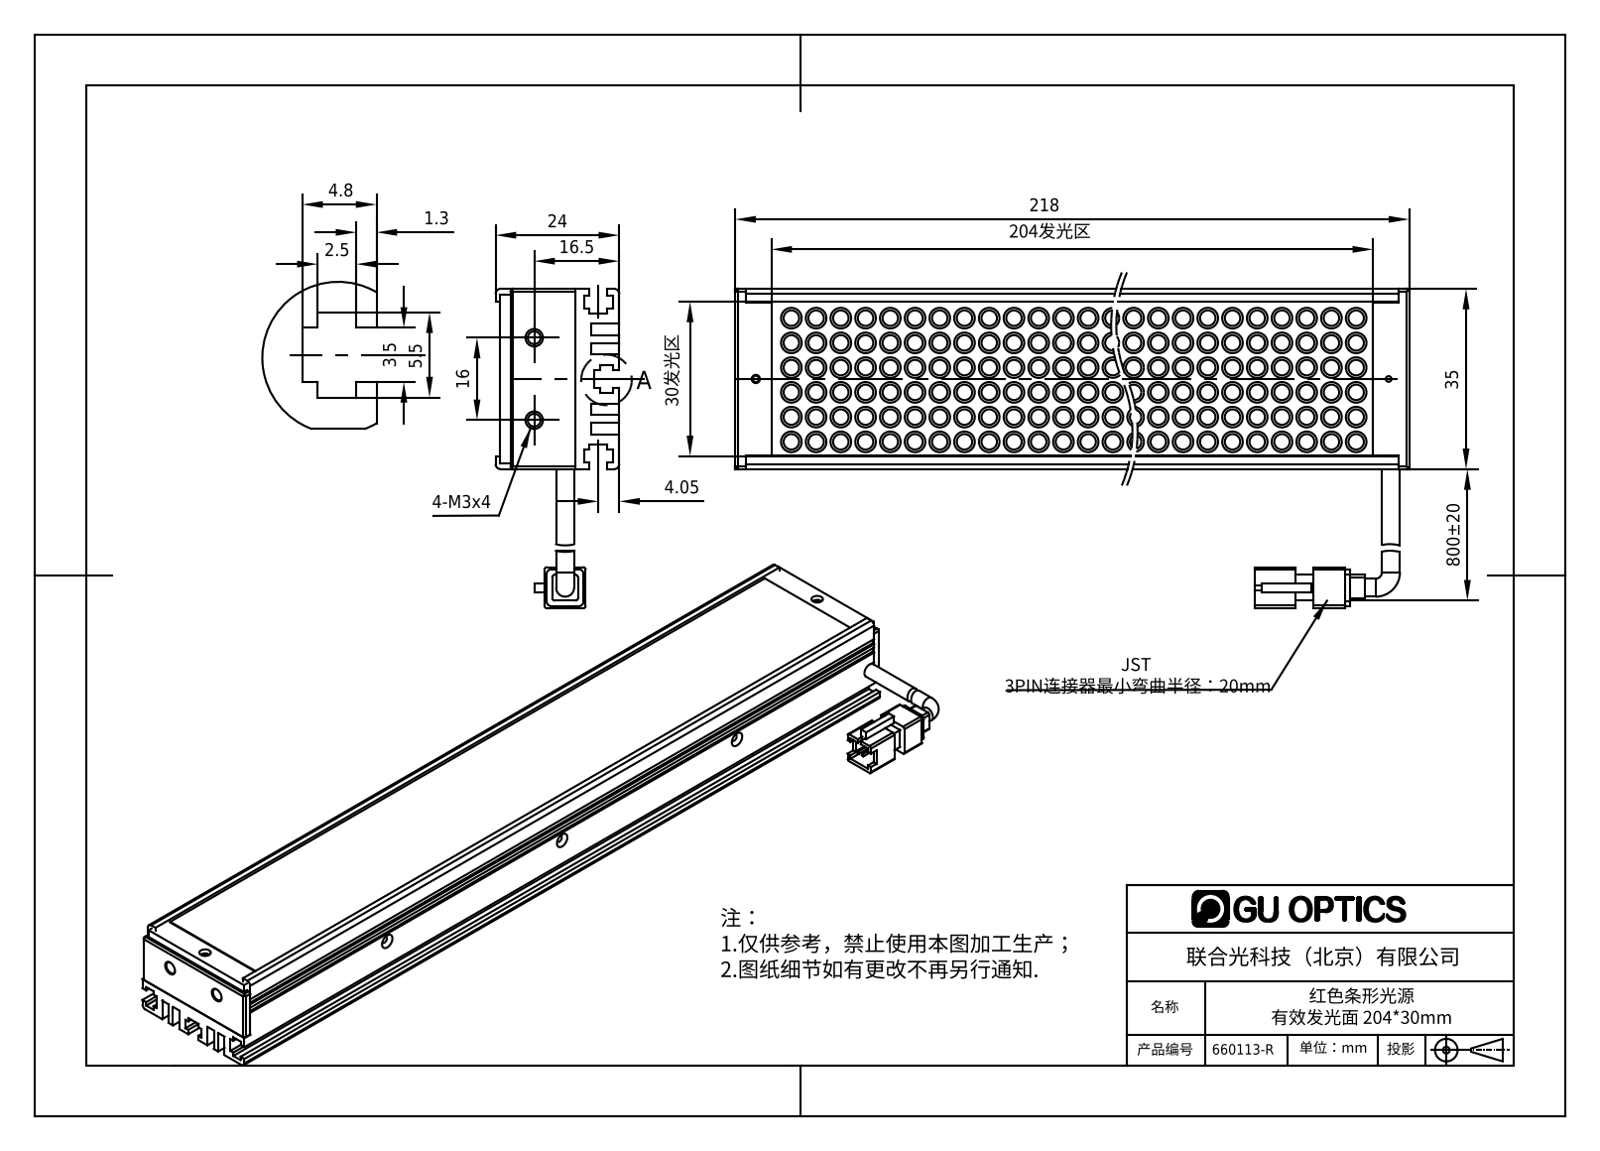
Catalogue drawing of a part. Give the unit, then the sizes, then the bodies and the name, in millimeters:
Units: millimetres
Overall size (bounding box): 218 × 62 × 24
Round holes (diameter × count): ⌀1.6 ×5, ⌀1.7 ×3, ⌀1.5 ×2, ⌀2.5 ×2, ⌀2.8 ×2, ⌀3 ×2, ⌀1.1 ×1, ⌀1.25 ×1, ⌀2 ×1
Round bosses / shafts (diameter × count): ⌀4 ×252, ⌀3 ×252, ⌀3.5 ×2
Partial cylindrical surfaces — rounded edges, fillets, slot ends (radius × count): R1 ×12, R0.5 ×8, R1.65 ×1
Main face-to-face distances: 2, 2.2, 8.6, 1, 2.5, 9, 4, 12.6, 14.6, 10.6
Hole centre spacings: 210, 7, 45.03, 45.32, 60, 105.01, 105.14, 165.01
Volume: 97 259 mm³ · Surface area: 110 838 mm²
Bodies: 8 solids, 1974 faces (520 planar, 1095 cylindrical, 359 other)
Part name (STEP PRODUCT): 660113-R
STEP written by: SolidWorks 2016 (AUTOMOTIVE_DESIGN)
